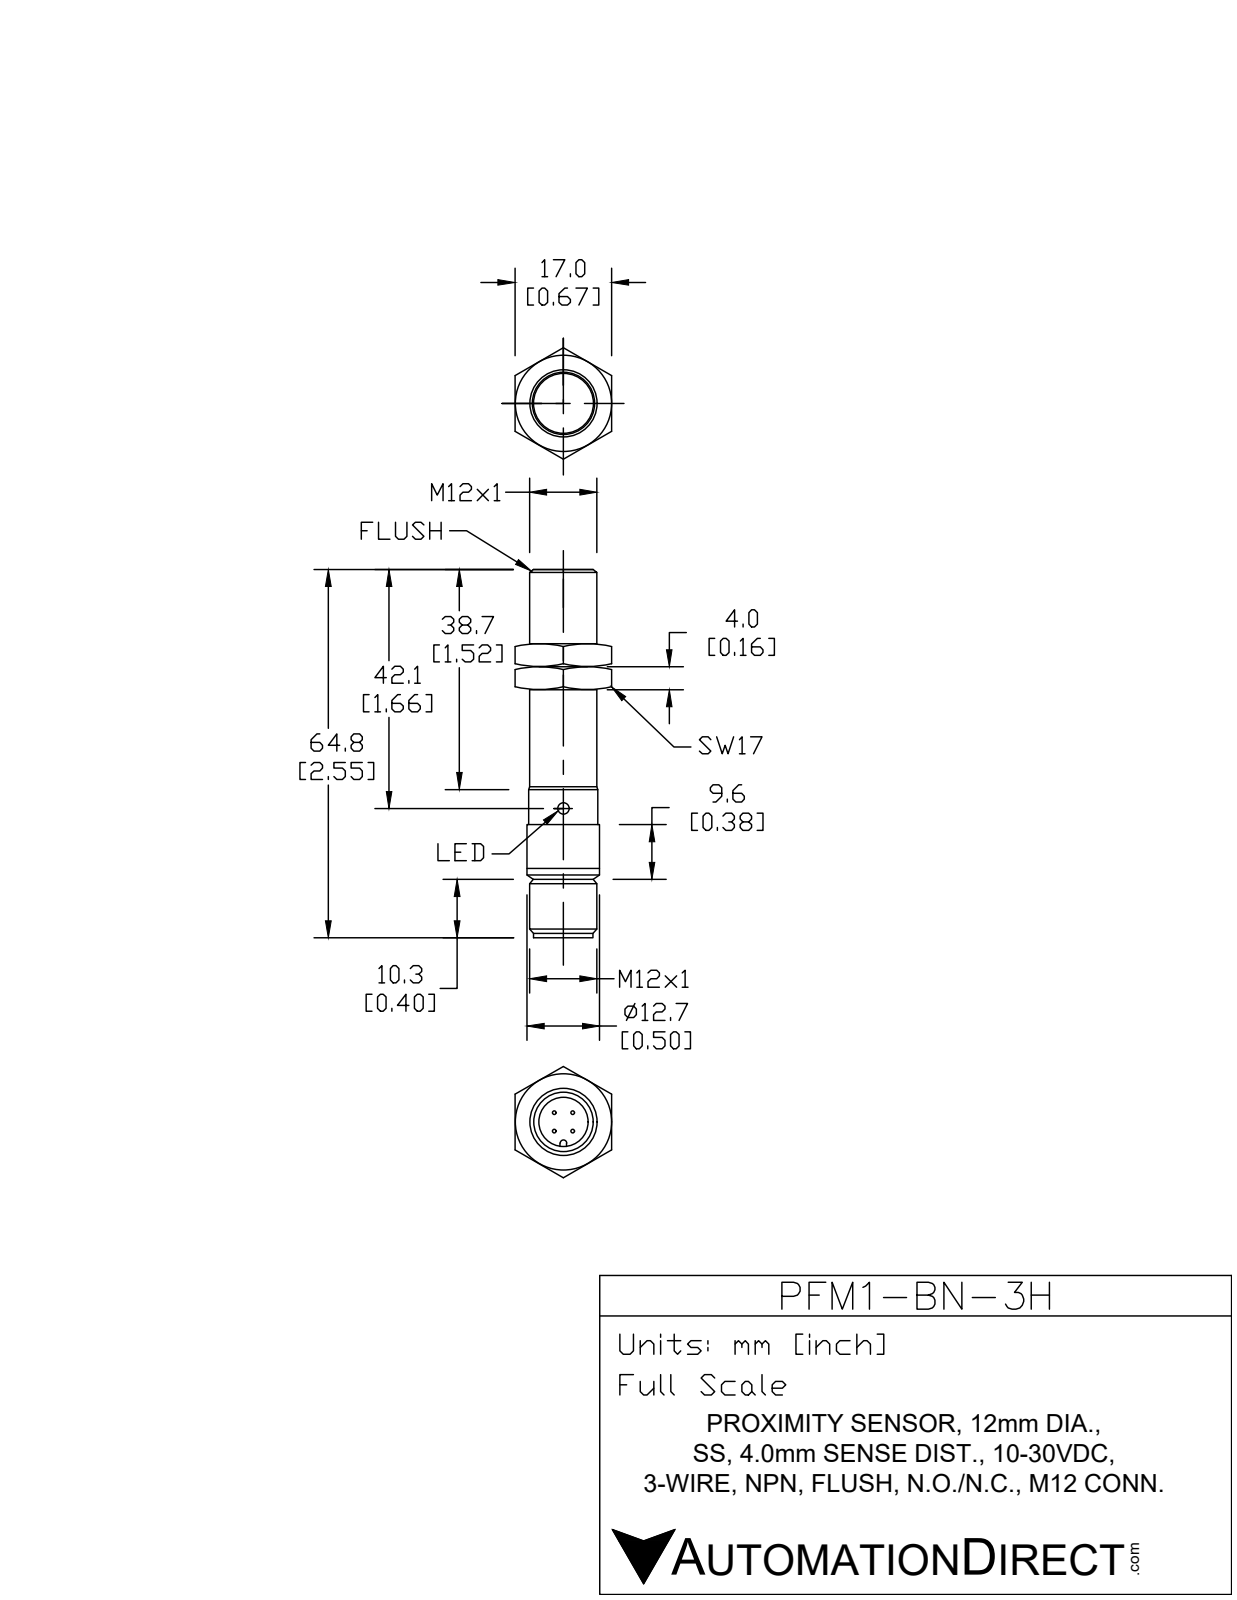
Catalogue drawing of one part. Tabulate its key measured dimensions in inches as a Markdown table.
| quantity | value |
| --- | --- |
| part name | PFM1-BN-3H |
| STEP written by | SolidWorks 2017 (AUTOMOTIVE_DESIGN) |
| units | inches |
| bodies | 3 solids, 70 faces (10 planar, 36 cylindrical, 24 other) |
| overall size | 2.543 × 0.5 × 0.5 |
| volume | 0.422 in³ |
| surface area | 6.12 in² |
| round holes (diameter × count) | 0.118 × 1, 0.331 × 1, 0.335 × 1, 0.374 × 1 |
| round bosses / shafts (diameter × count) | 0.039 × 4, 0.5 × 1, 0.472 × 1, 0.413 × 1, 0.396 × 1, 0.37 × 1 |
| partial cylindrical surfaces (radius × count) | 0.024 × 1, 0.219 × 1 |
| main face-to-face distances | 0.071, 2.075, 2.146, 2.193, 0.118, 0.047, 2.504, 0.429, 0.358, 0.311 |
